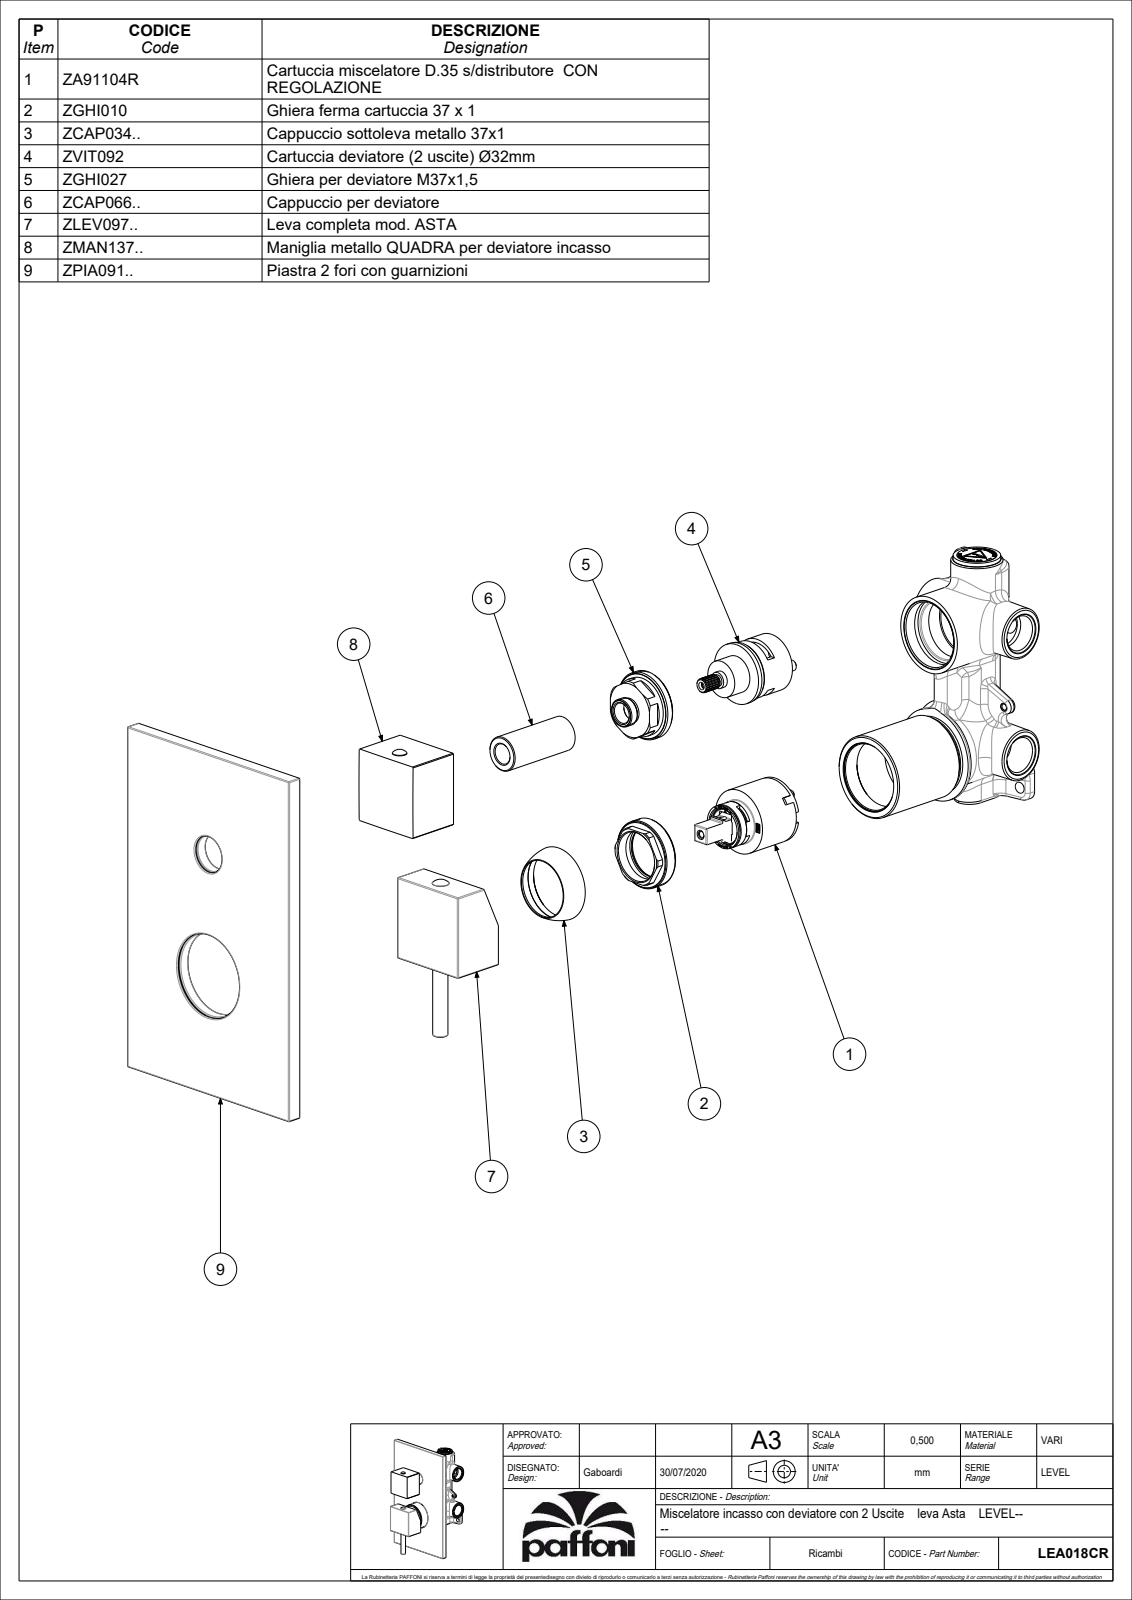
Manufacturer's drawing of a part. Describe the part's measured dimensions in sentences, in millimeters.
The part is named "LEA018CR". Its 3-D file was written by "CREO PARAMETRIC BY PTC INC, 2020044 (CONFIG_CONTROL_DESIGN)". It is 4 solids with 1095 faces: 634 planar, 276 cylindrical and 185 other. Overall it measures 190 by 120 by 56.39 millimeters. Its volume is 195 380 cubic millimeters and its surface area 132 605 square millimeters. Round holes: 2 of diameter 4, 2 of diameter 5.5, 2 of diameter 36, 1 of diameter 3, 1 of diameter 3.2, 1 of diameter 3.3, 1 of diameter 4.2, 1 of diameter 4.5, 1 of diameter 5, 1 of diameter 6, 1 of diameter 8.1, 1 of diameter 11. Round bosses or shafts: 2 of diameter 5, 1 of diameter 51, 1 of diameter 49, 1 of diameter 44.8, 1 of diameter 35, 1 of diameter 25, 1 of diameter 23.5, 1 of diameter 23.4. Partial cylindrical surfaces (rounded edges, fillets, slot ends): 24 of radius 0.5, 11 of radius 0.15, 10 of radius 1, 4 of radius 0.3, 1 of radius 7, 1 of radius 9.3, 1 of radius 10.85, 1 of radius 11.25. The main face-to-face distances are 2.5, 5.5, 8, 0.5, 3, 5, 40, 47.1, 37.5, 80. The hole center spacings are 10, 14.6, 14.8, 58, 68.
